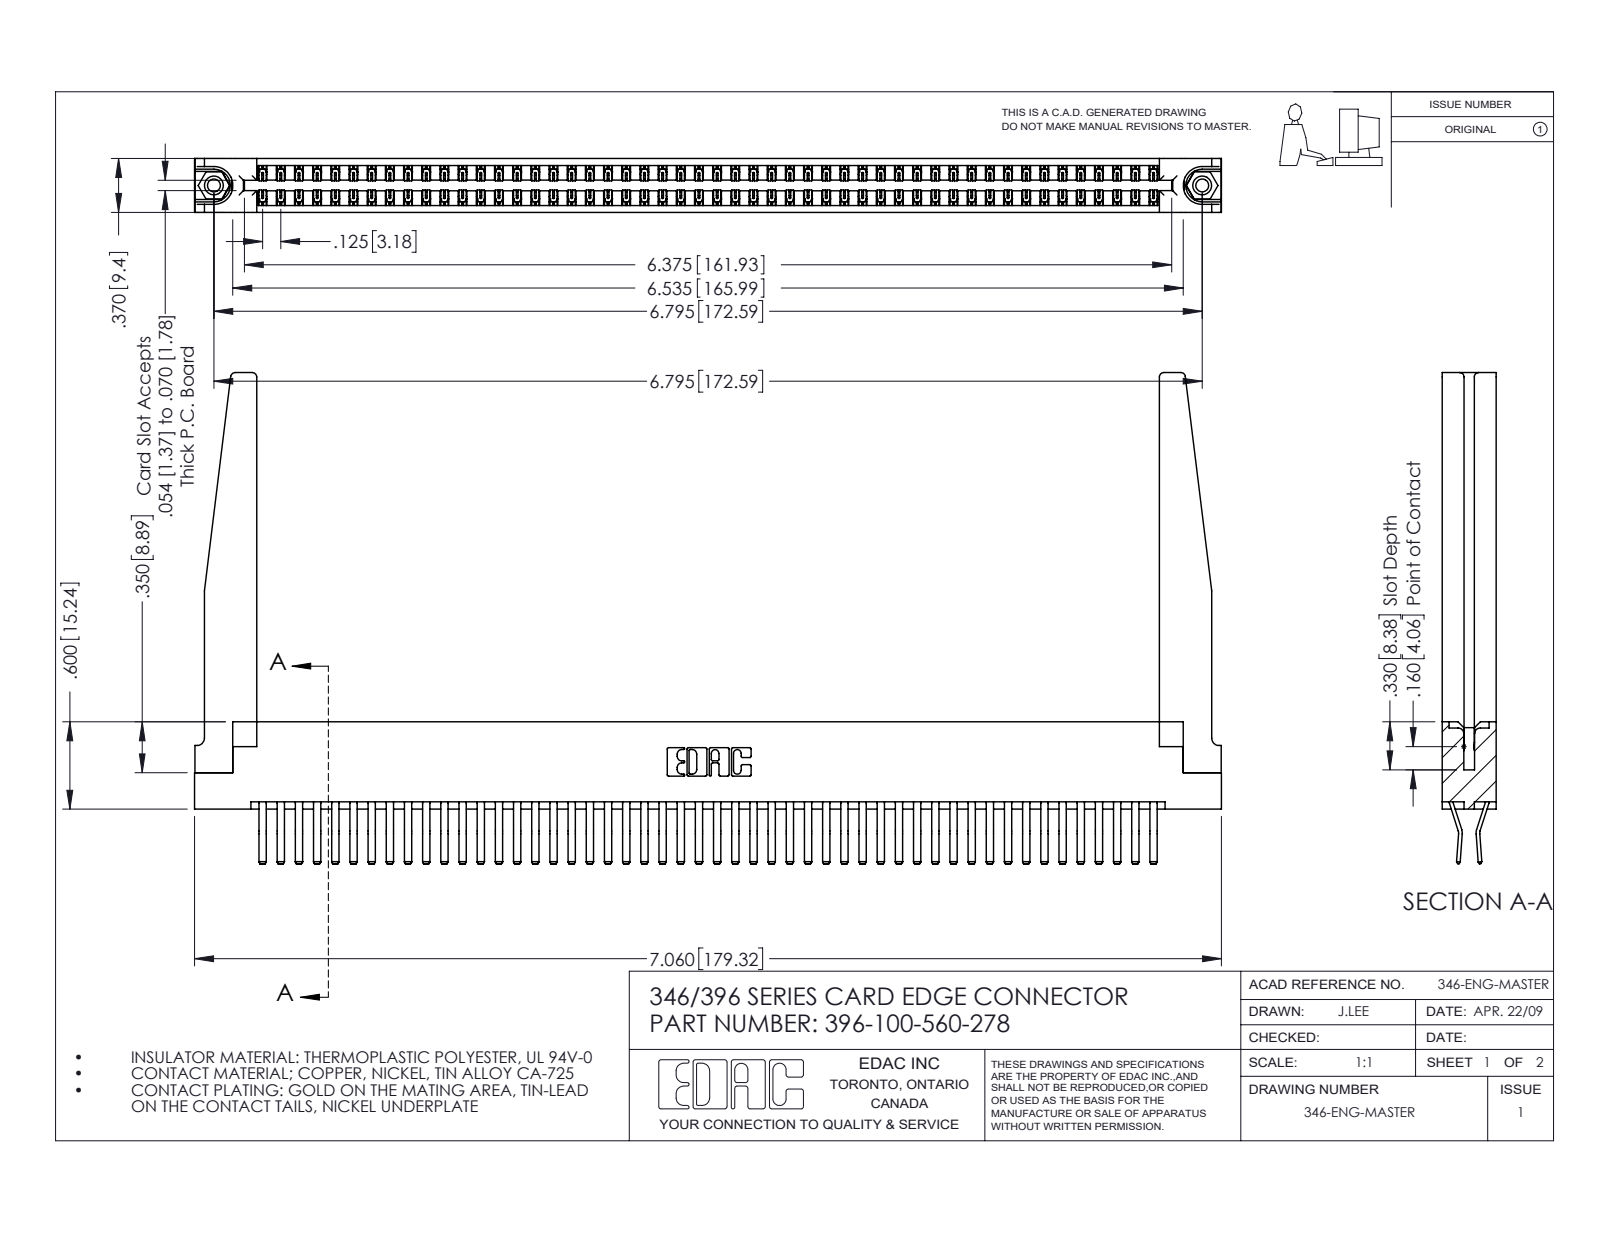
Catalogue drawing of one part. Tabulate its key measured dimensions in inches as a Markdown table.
| quantity | value |
| --- | --- |
| part name | 346 Part_Flush Mounting Lugs - 0.156 Dia-TH; 345-250-001_345-250-001-102; 396-100-560-278; 346-220-078_345-220-078 (+1 more) |
| STEP written by | SolidWorks 2016 (CONFIG_CONTROL_DESIGN) |
| units | inches |
| bodies | 105 solids, 5756 faces (3718 planar, 1986 cylindrical, 52 other) |
| overall size | 7.06 × 3.375 × 0.37 |
| volume | 1.532 in³ |
| surface area | 51.82 in² |
| round holes (diameter × count) | 0.089 × 2, 0.125 × 2, 0.156 × 2, 0.064 × 1 |
| round bosses / shafts (diameter × count) | 0.155 × 2 |
| partial cylindrical surfaces (radius × count) | 0.006 × 150, 0.01 × 22, 0.03 × 8, 0.007 × 6, 0.031 × 6, 0.05 × 4, 0.026 × 3, 0.01 × 2 |
| main face-to-face distances | 0.37, 0.048, 0.322, 0.025, 0.072, 0.25, 0.148, 0.15, 0.298, 0.275 |
| hole center spacings | 0.246, 6.586, 6.795 |
